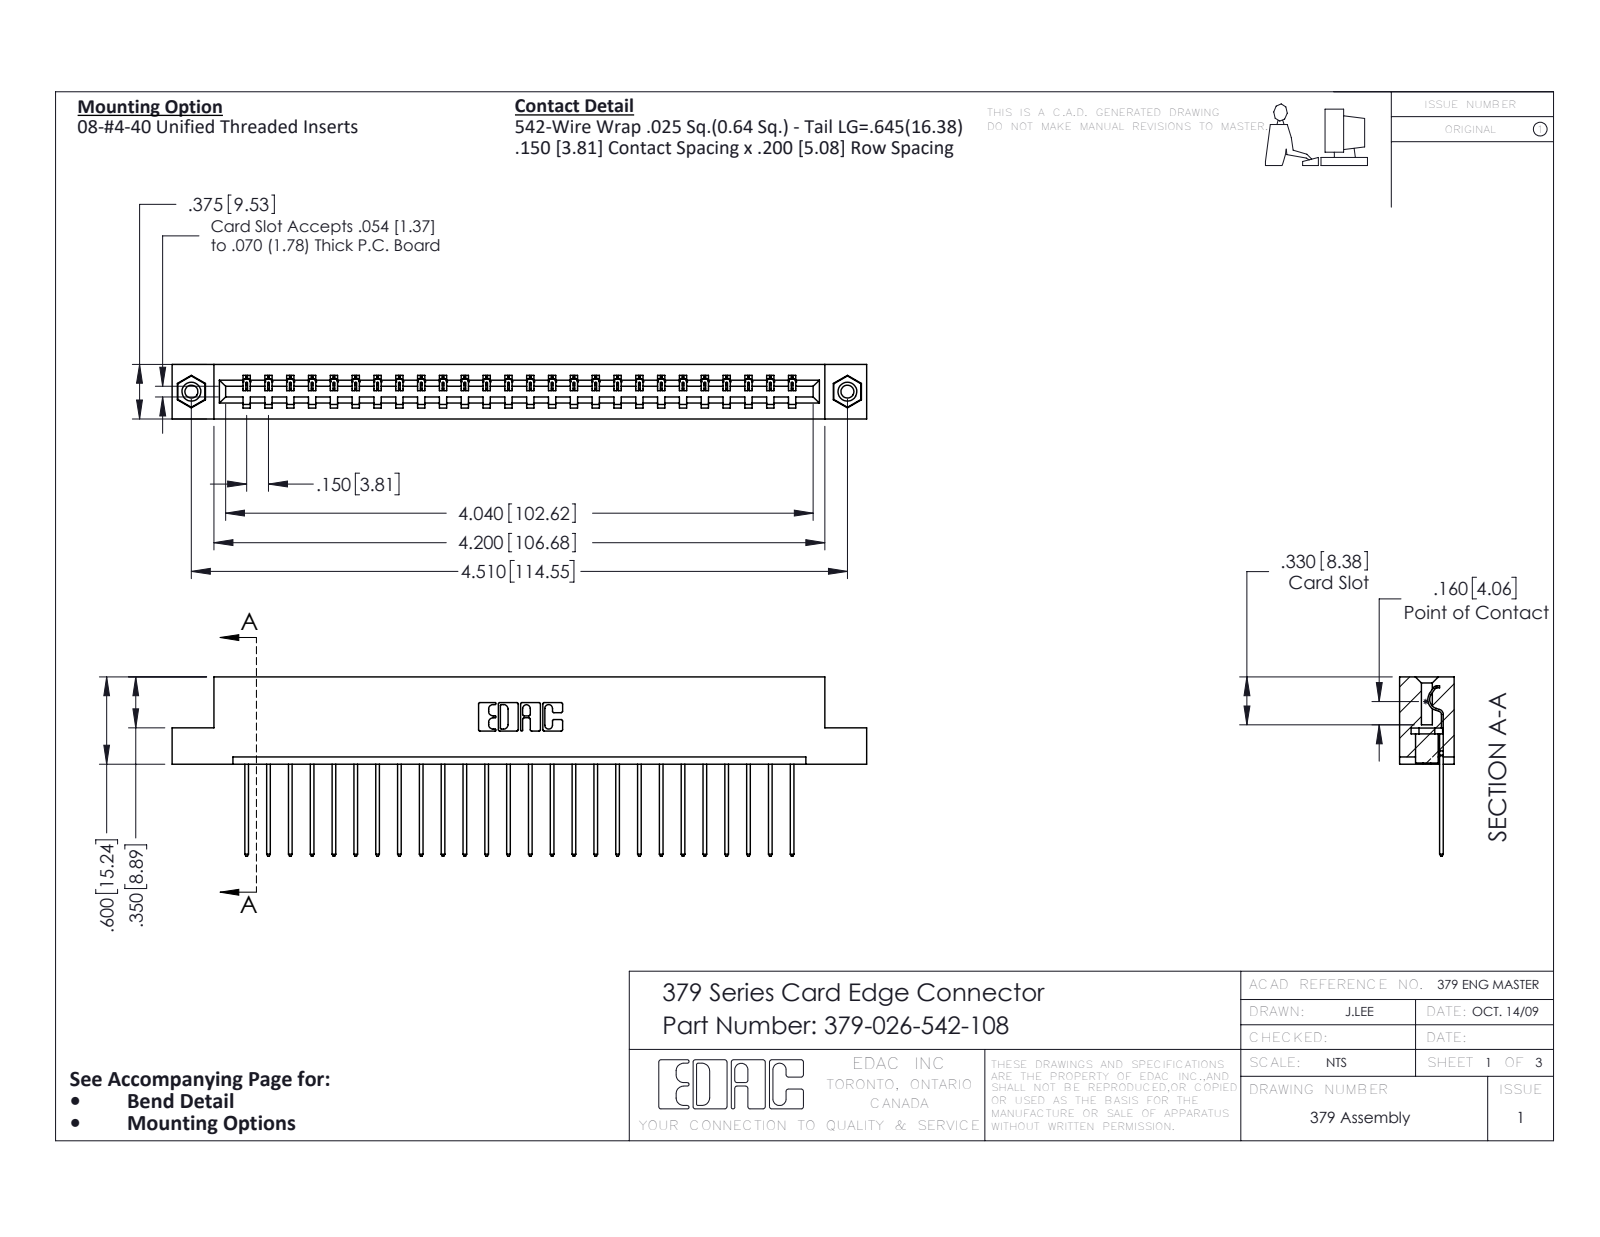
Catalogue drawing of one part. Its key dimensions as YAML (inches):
part_name: "379 Part_Flush - .156 Dia - TI; 345-250-001_345-250-003-102; 345-292-001_345-293-142; 379-026-542-108"
step_written_by: "SolidWorks 2016 (CONFIG_CONTROL_DESIGN)"
units: inches
bodies: {solids: 29, faces: 1682, planar: 1194, cylindrical: 472, other: 16}
overall_size: [4.775, 1.232, 0.375]
volume: 0.769
surface_area: 20.5
round_holes:
  - {diameter: 0.089, count: 2}
  - {diameter: 0.125, count: 2}
  - {diameter: 0.156, count: 2}
round_bosses_or_shafts:
  - {diameter: 0.155, count: 2}
partial_cylinders:
  - {radius: 0.006, count: 52}
  - {radius: 0.01, count: 52}
  - {radius: 0.01, count: 22}
  - {radius: 0.007, count: 6}
  - {radius: 0.031, count: 6}
  - {radius: 0.026, count: 3}
  - {radius: 0.014, count: 1}
  - {radius: 0.022, count: 1}
face_to_face_distances: [0.3, 0.075, 0.375, 0.225, 0.6, 0.275, 0.1, 0.025, 0.2, 0.15]
hole_center_spacings: [4.51]
